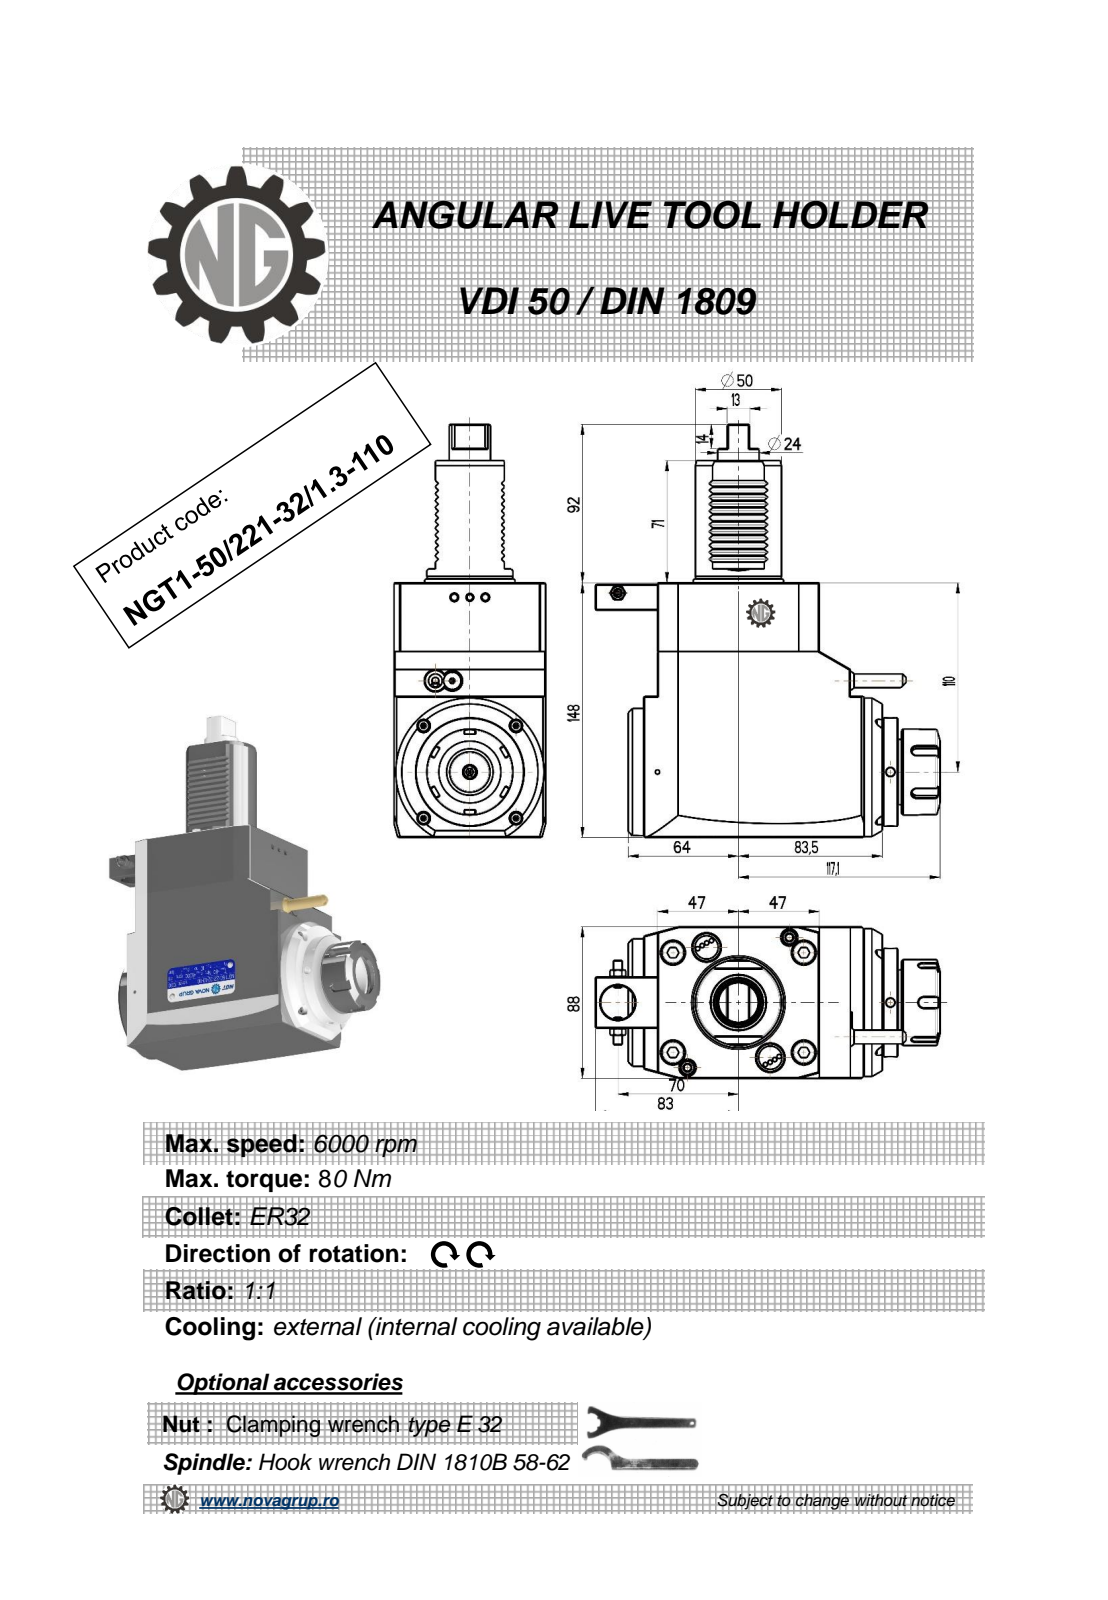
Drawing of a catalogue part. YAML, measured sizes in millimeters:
part_name: "NGT1_50_221_32_1_3_110"
step_written_by: "PRO/ENGINEER BY PARAMETRIC TECHNOLOGY CORPORATION, 2010280 (CONFIG_CONTROL_DESIGN)"
units: millimeters
bodies: {solids: 1, faces: 460, planar: 235, cylindrical: 103, other: 122}
overall_size: [240, 200.1, 88]
volume: 1794000
surface_area: 112441
round_holes:
  - {diameter: 5, count: 3}
  - {diameter: 3, count: 1}
  - {diameter: 9.5, count: 1}
  - {diameter: 20, count: 1}
  - {diameter: 27, count: 1}
round_bosses_or_shafts:
  - {diameter: 50, count: 2}
  - {diameter: 86, count: 1}
  - {diameter: 74, count: 1}
  - {diameter: 63, count: 1}
  - {diameter: 41, count: 1}
  - {diameter: 24, count: 1}
  - {diameter: 10, count: 1}
  - {diameter: 8.96, count: 1}
partial_cylinders:
  - {radius: 0.3, count: 24}
  - {radius: 0.26, count: 12}
  - {radius: 0.2, count: 6}
  - {radius: 3, count: 5}
  - {radius: 0.8, count: 2}
  - {radius: 2.5, count: 1}
face_to_face_distances: [88, 148, 147.5, 9, 17, 8, 94, 111, 130.5, 36.5]
hole_center_spacings: [52.46, 56.65, 101.5, 158.25]
